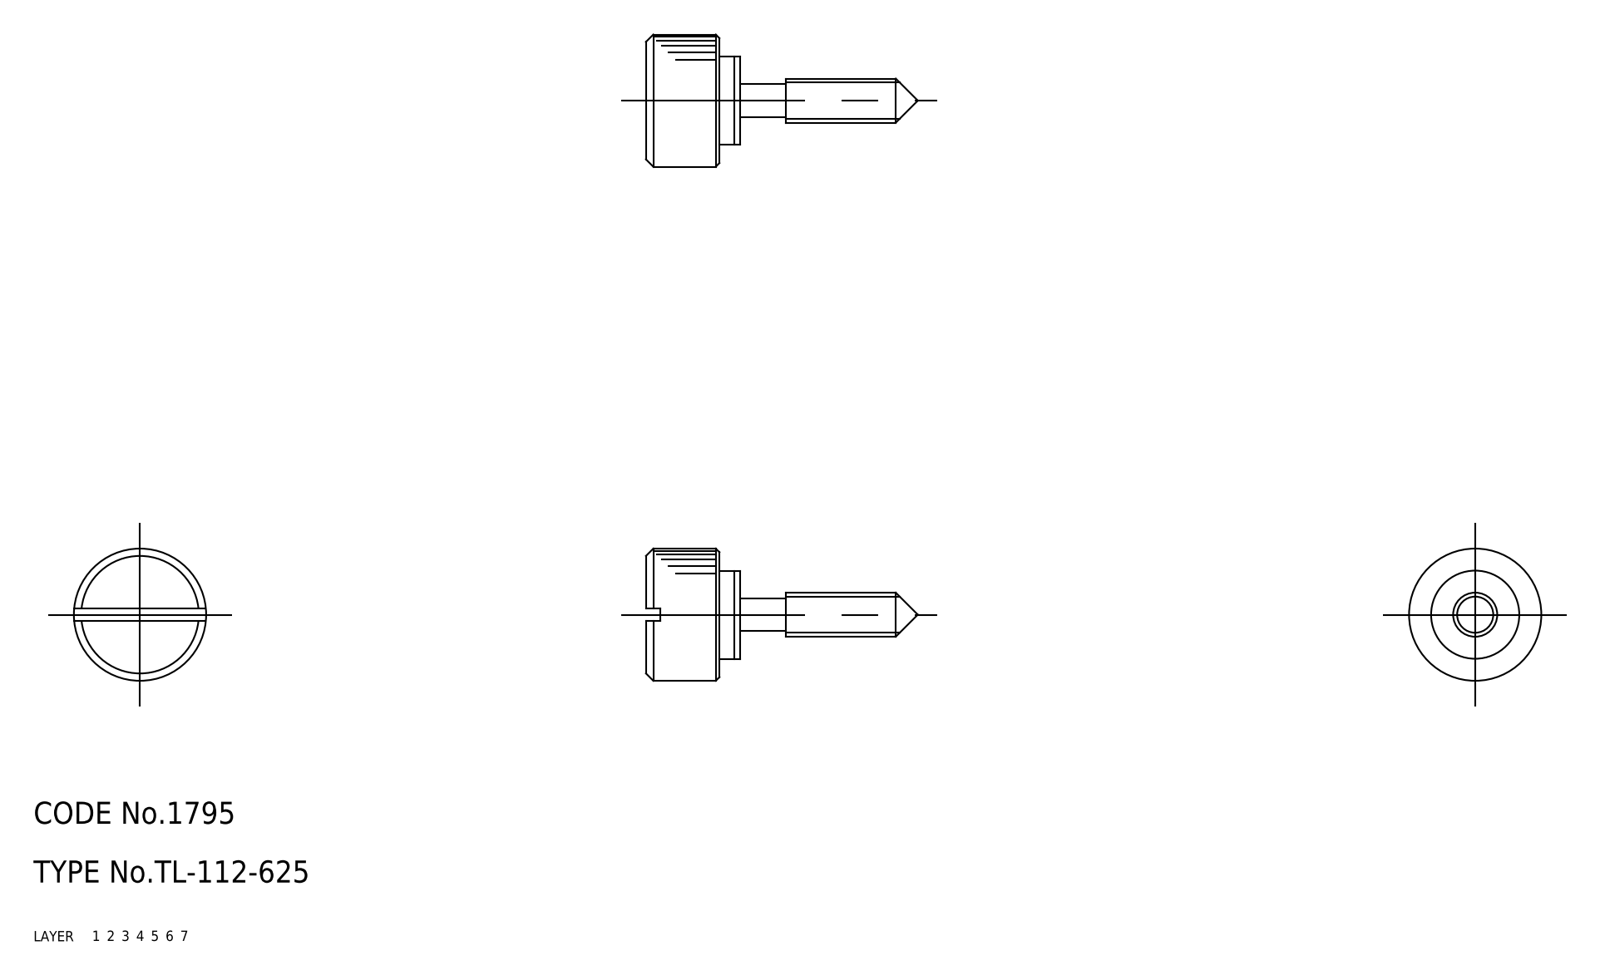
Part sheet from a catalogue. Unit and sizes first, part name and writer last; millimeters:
Units: millimetres
Overall size (bounding box): 37 × 18 × 18
Volume: 3 314 mm³ · Surface area: 1 801 mm²
Bodies: 2 solids, 42 faces (0 planar, 0 cylindrical, 42 other)
Part name (STEP PRODUCT): washer; knob; TL_112_625_8896_36
STEP written by: CADfix (AUTOMOTIVE_DESIGN)
